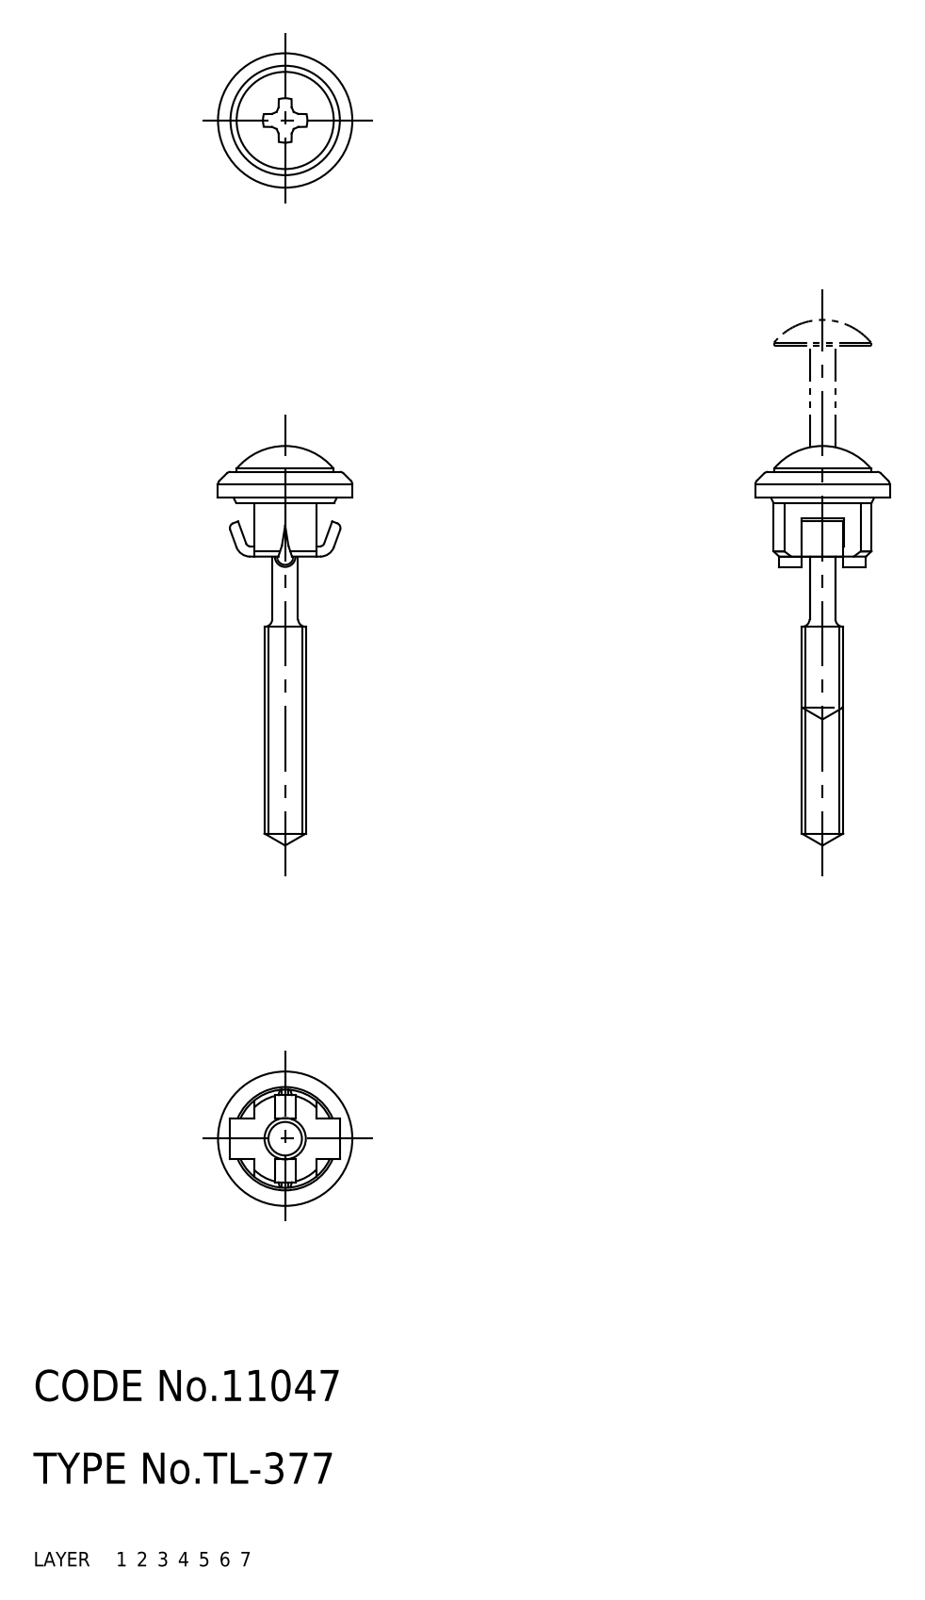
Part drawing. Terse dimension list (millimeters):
name: 67114927; 67114940
written by: CADfix (AUTOMOTIVE_DESIGN)
unit: mm
bodies: 2 solids, 121 faces (0 planar, 0 cylindrical, 121 other)
size: 38.54 × 13 × 13
volume: 946 mm³; area: 1 305 mm²
